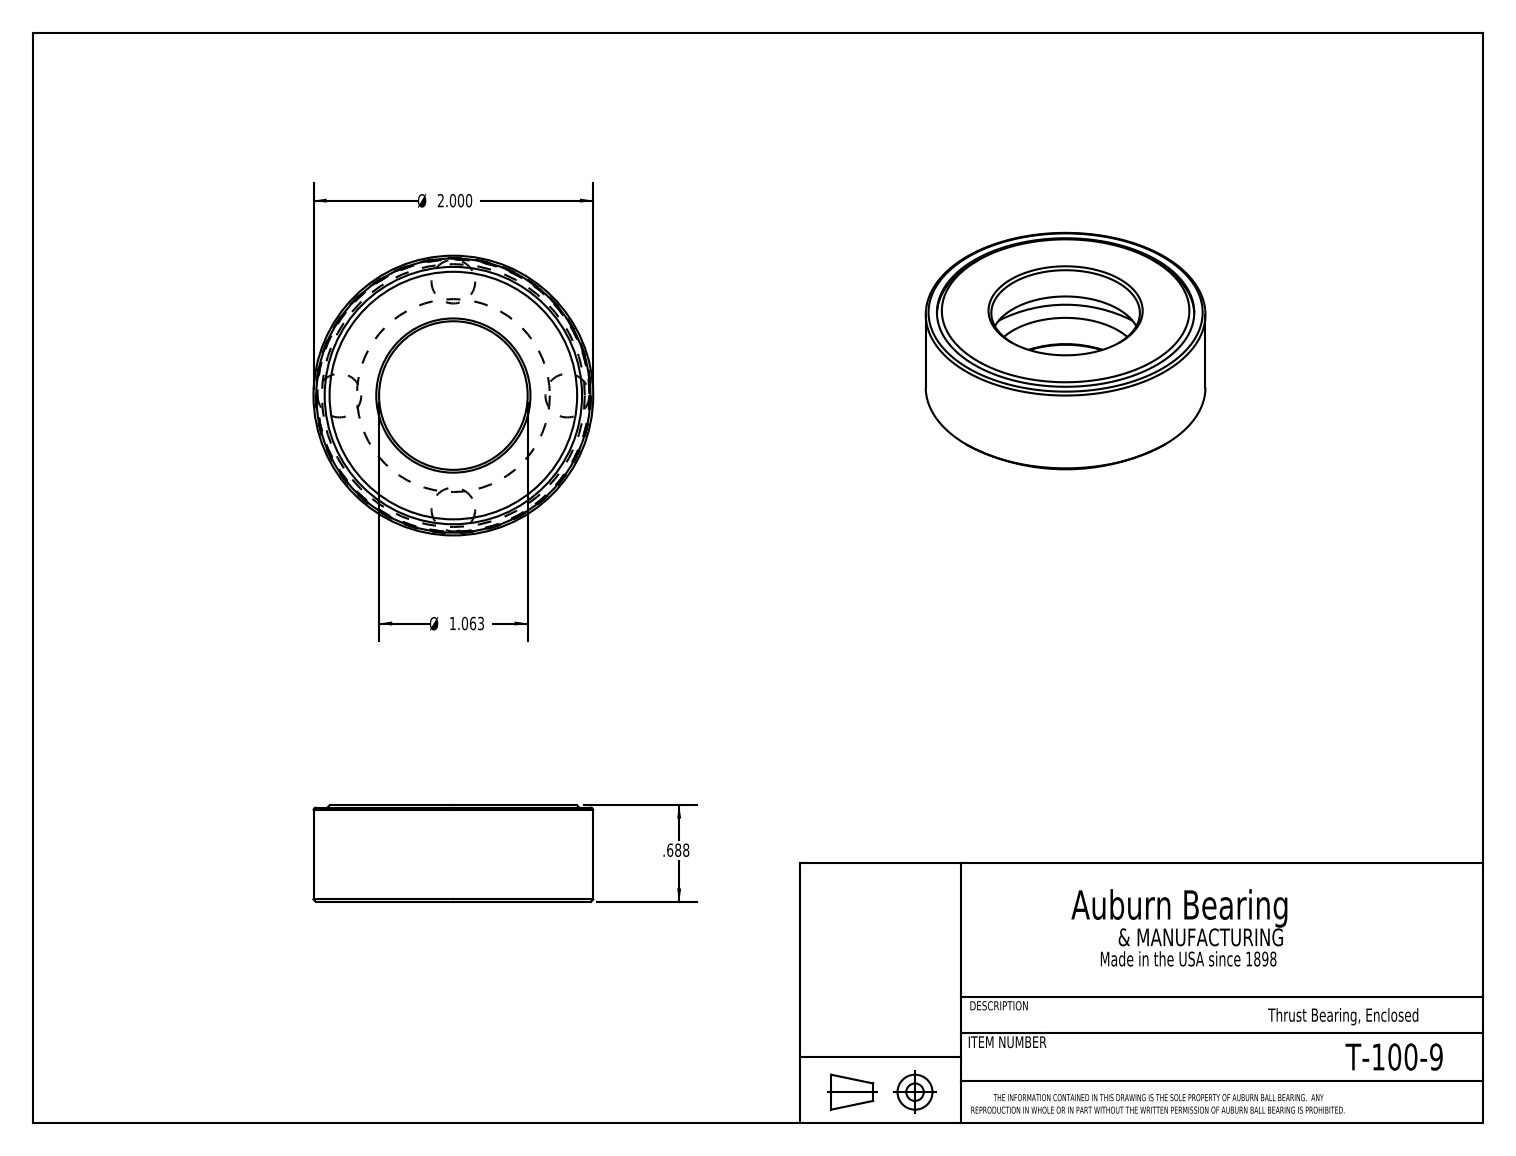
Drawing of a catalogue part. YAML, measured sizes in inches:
part_name: "T-100-9"
step_written_by: "SolidWorks 2016 (CONFIG_CONTROL_DESIGN)"
units: inches
bodies: {solids: 6, faces: 28, planar: 9, cylindrical: 7, other: 12}
overall_size: [2, 2, 0.688]
volume: 1.072
surface_area: 20.58
round_holes:
  - {diameter: 1.063, count: 1}
  - {diameter: 1.84, count: 1}
  - {diameter: 1.96, count: 1}
round_bosses_or_shafts:
  - {diameter: 2, count: 1}
  - {diameter: 1.946, count: 1}
face_to_face_distances: [0.25, 0.437, 0.687, 0.187, 0.652, 0.402, 0.215, 0.035, 0.672, 0.422]
